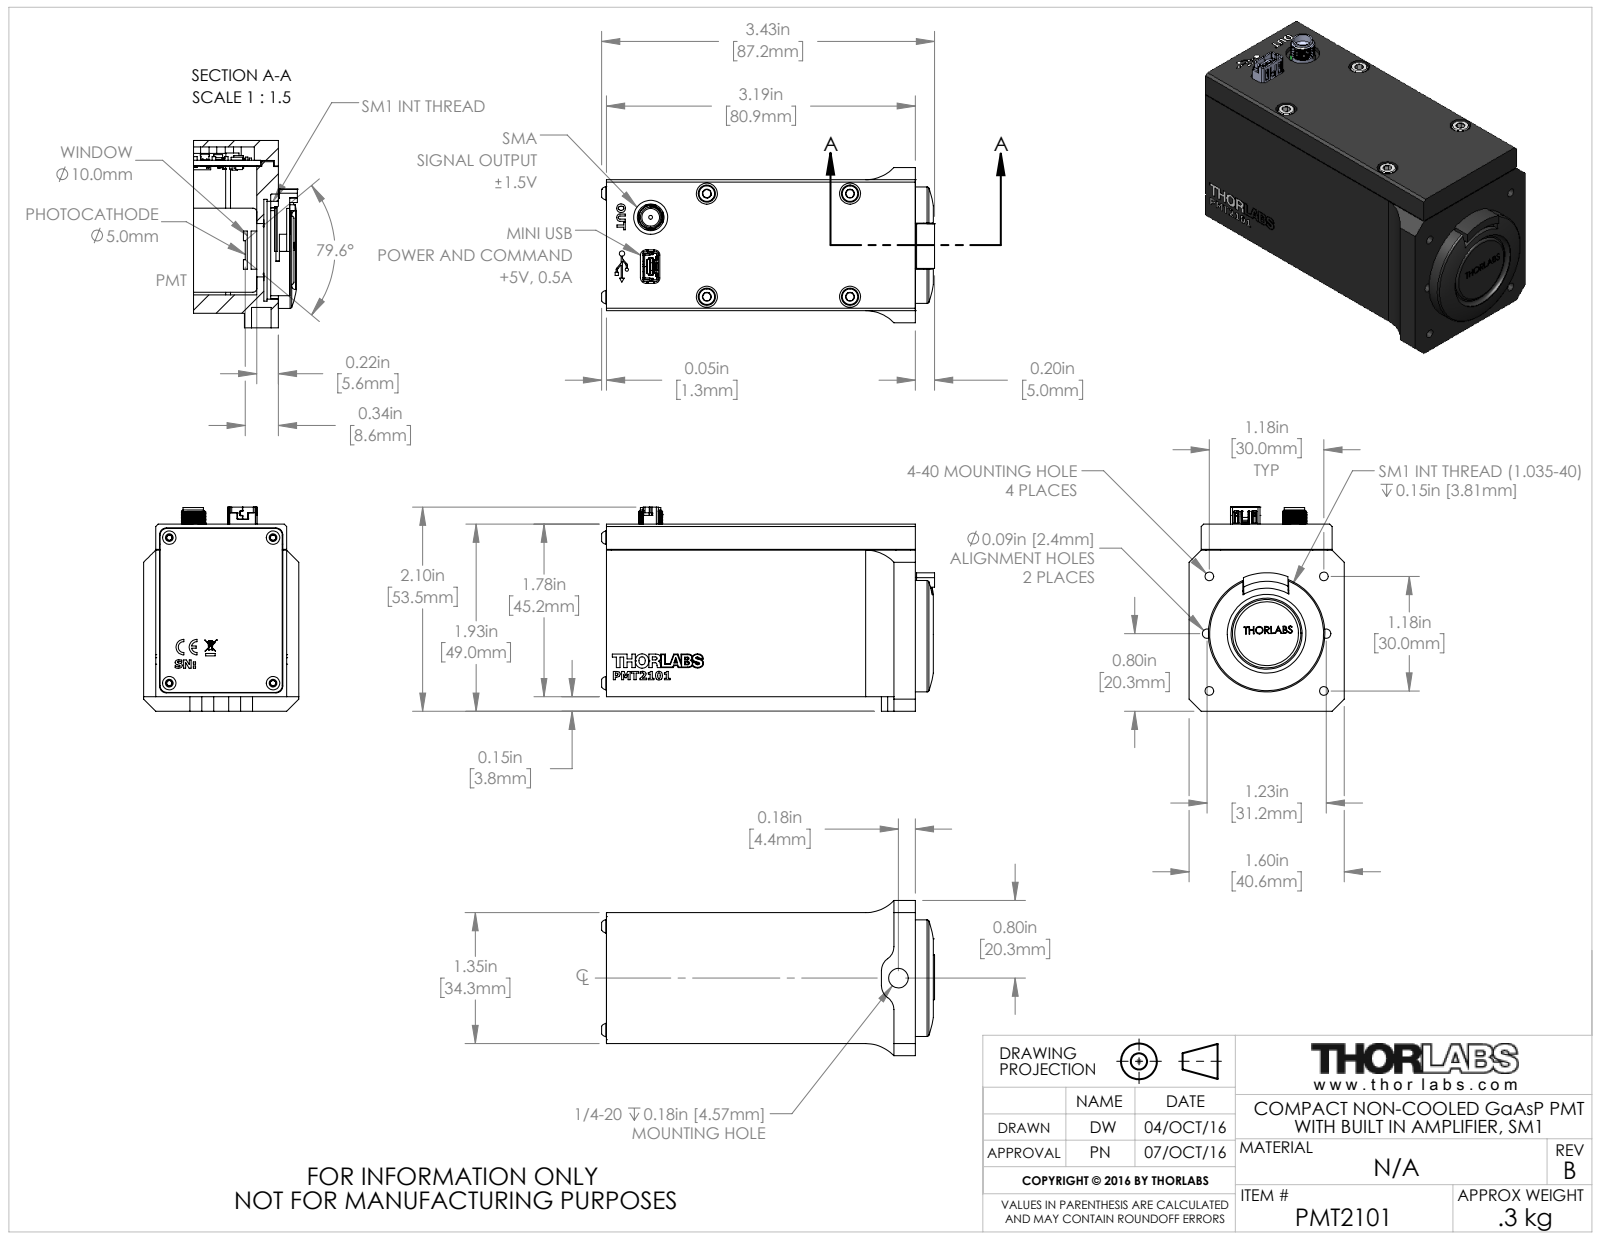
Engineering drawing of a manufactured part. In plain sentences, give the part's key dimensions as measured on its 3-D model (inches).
The part is named "TTN092697-E0W". Its 3-D file was written by "SolidWorks 2016 (AUTOMOTIVE_DESIGN)". It is 0 solids with 7298 faces: 4002 planar, 2313 cylindrical and 983 other. Overall it measures 3.433 by 2.105 by 1.6 inches. Round holes: 9 of diameter 0.063, 8 of diameter 0.094, 5 of diameter 0.024, 5 of diameter 0.067, 5 of diameter 0.114, 4 of diameter 0.081, 4 of diameter 0.089, 4 of diameter 0.173, 4 of diameter 0.217, 2 of diameter 0.016, 2 of diameter 0.035, 2 of diameter 0.079. Round bosses or shafts: 9 of diameter 0.138, 8 of diameter 0.079, 8 of diameter 0.058, 8 of diameter 0.02, 4 of diameter 0.177, 4 of diameter 0.098, 4 of diameter 0.075, 4 of diameter 0.047. Partial cylindrical surfaces (rounded edges, fillets, slot ends): 87 of radius 0.004, 34 of radius 0.008, 24 of radius 0.02, 20 of radius 0.07, 20 of radius 0.135, 10 of radius 0.015, 8 of radius 0.15, 6 of radius 0.01. The main face-to-face distances are 0.215, 1.135, 1.35, 0.893, 0.027, 0.866, 1.78, 0.058, 0.92, 1.577. The hole center spacings are 0.922, 0.145, 0.513, 0.551, 0.063, 0.078, 0.205, 0.39.
